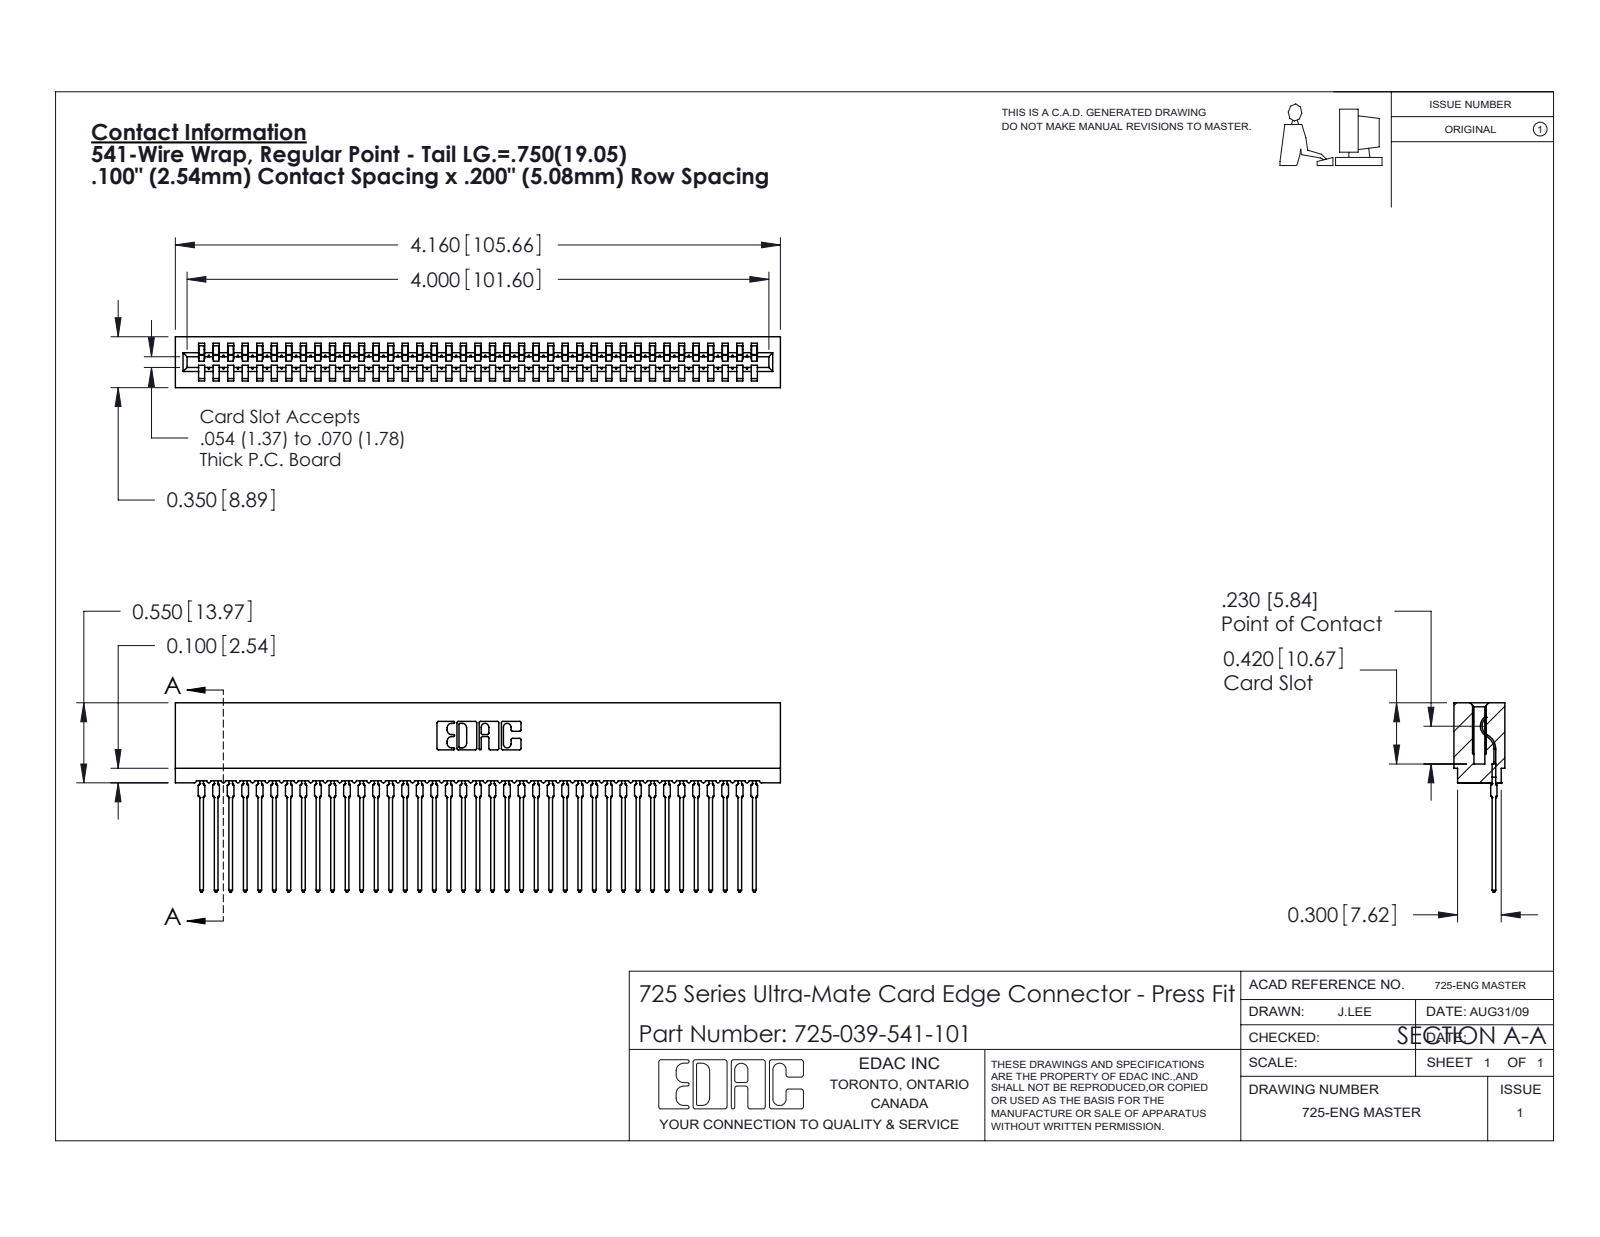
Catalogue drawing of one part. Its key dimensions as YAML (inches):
part_name: "745-292-001_541; 725 Part_Insulator Option - 01; 725-039-541-101"
step_written_by: "SolidWorks 2020 (CONFIG_CONTROL_DESIGN)"
units: inches
bodies: {solids: 40, faces: 4463, planar: 2668, cylindrical: 781, other: 1014}
overall_size: [4.16, 1.301, 0.35]
volume: 0.501
surface_area: 25.56
partial_cylinders:
  - {radius: 0.015, count: 78}
  - {radius: 0.021, count: 78}
  - {radius: 0.01, count: 22}
  - {radius: 0.007, count: 6}
  - {radius: 0.031, count: 6}
  - {radius: 0.005, count: 4}
  - {radius: 0.011, count: 4}
  - {radius: 0.026, count: 3}
face_to_face_distances: [0.35, 0.063, 0.287, 0.2, 0.212, 0.138, 0.1, 0.045, 0.305, 0.093]
